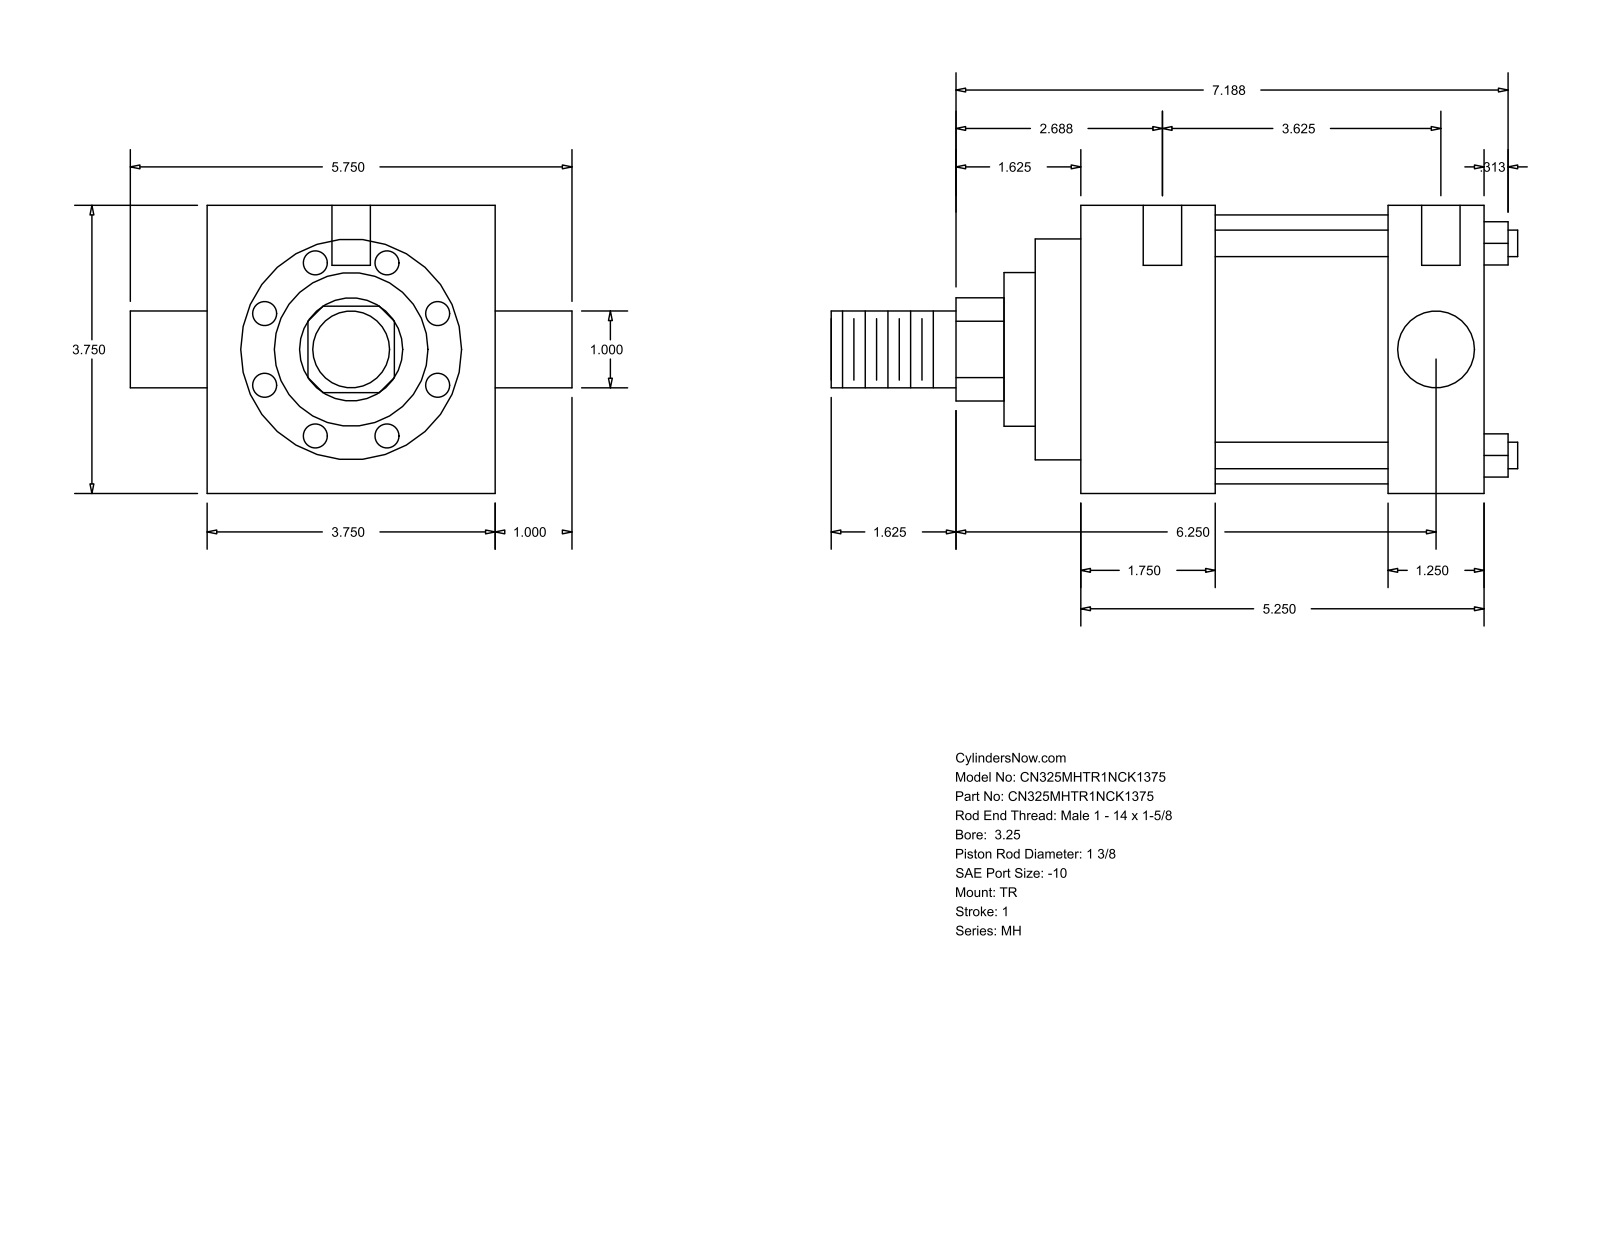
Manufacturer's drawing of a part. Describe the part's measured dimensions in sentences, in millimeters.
The part is named "MH_TR__0325_1.375". Its 3-D file was written by "GSSL Pune (CONFIG_CONTROL_DESIGN)". It is 0 solids with 86 faces: 61 planar, 25 cylindrical and 0 other. Overall it measures 227.01 by 146.05 by 95.25 millimeters. Round holes: 3 of diameter 5.56, 2 of diameter 12.7. Round bosses or shafts: 4 of diameter 8.76, 2 of diameter 25.4, 1 of diameter 88.9, 1 of diameter 73.03, 1 of diameter 50.8, 1 of diameter 34.92. Partial cylindrical surfaces (rounded edges, fillets, slot ends): 1 of radius 17.06. The main face-to-face distances are 95.24, 133.35, 44.45, 101.61, 57.16, 88.9, 31.74, 15.08, 59.53, 116.69. The hole center spacings are 1.59, 4.76, 92.08, 93.67, 96.84, 98.43.
